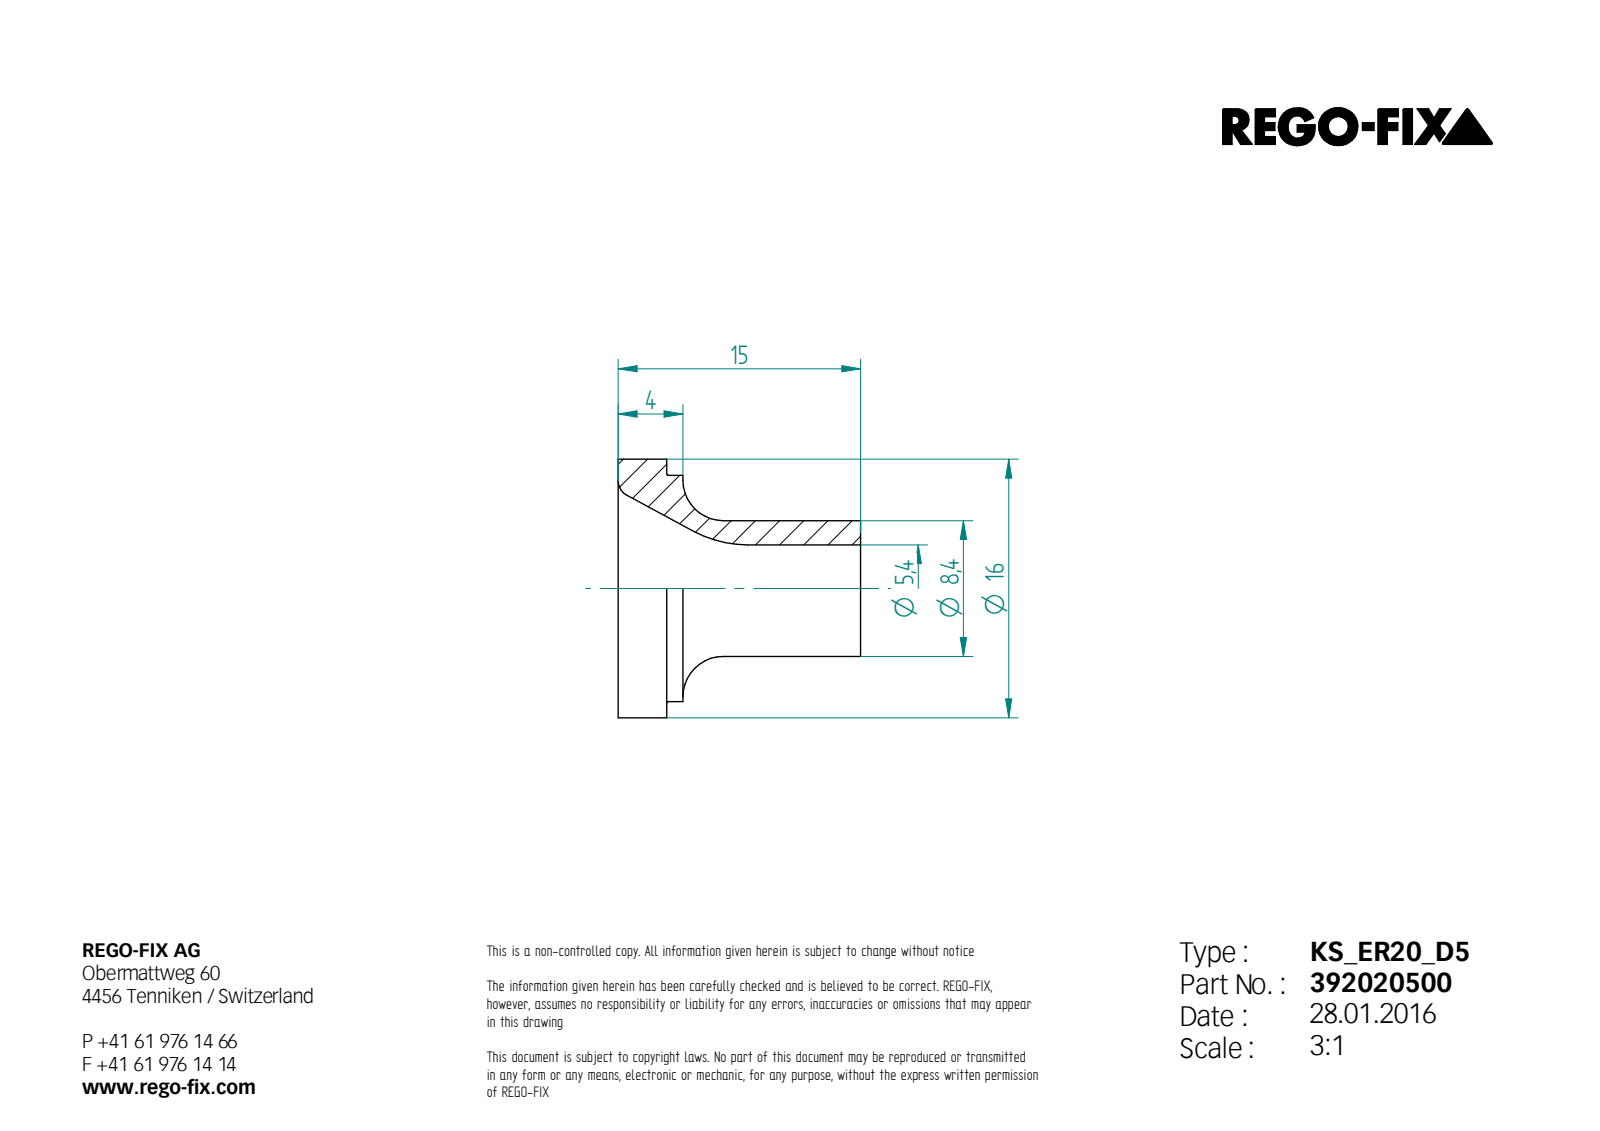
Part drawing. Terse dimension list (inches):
written by: Unknown (AUTOMOTIVE_DESIGN)
unit: in
bodies: 1 solid, 13 faces (4 planar, 4 cylindrical, 5 other)
size: 0.63 × 0.63 × 0.591
volume: 0.049 in³; area: 1.645 in²
holes: 1× ⌀0.213
bosses: 1× ⌀0.63, 1× ⌀0.551, 1× ⌀0.331
face distances: 0.118, 0.591, 0.472, 0.157, 0.039, 0.433
